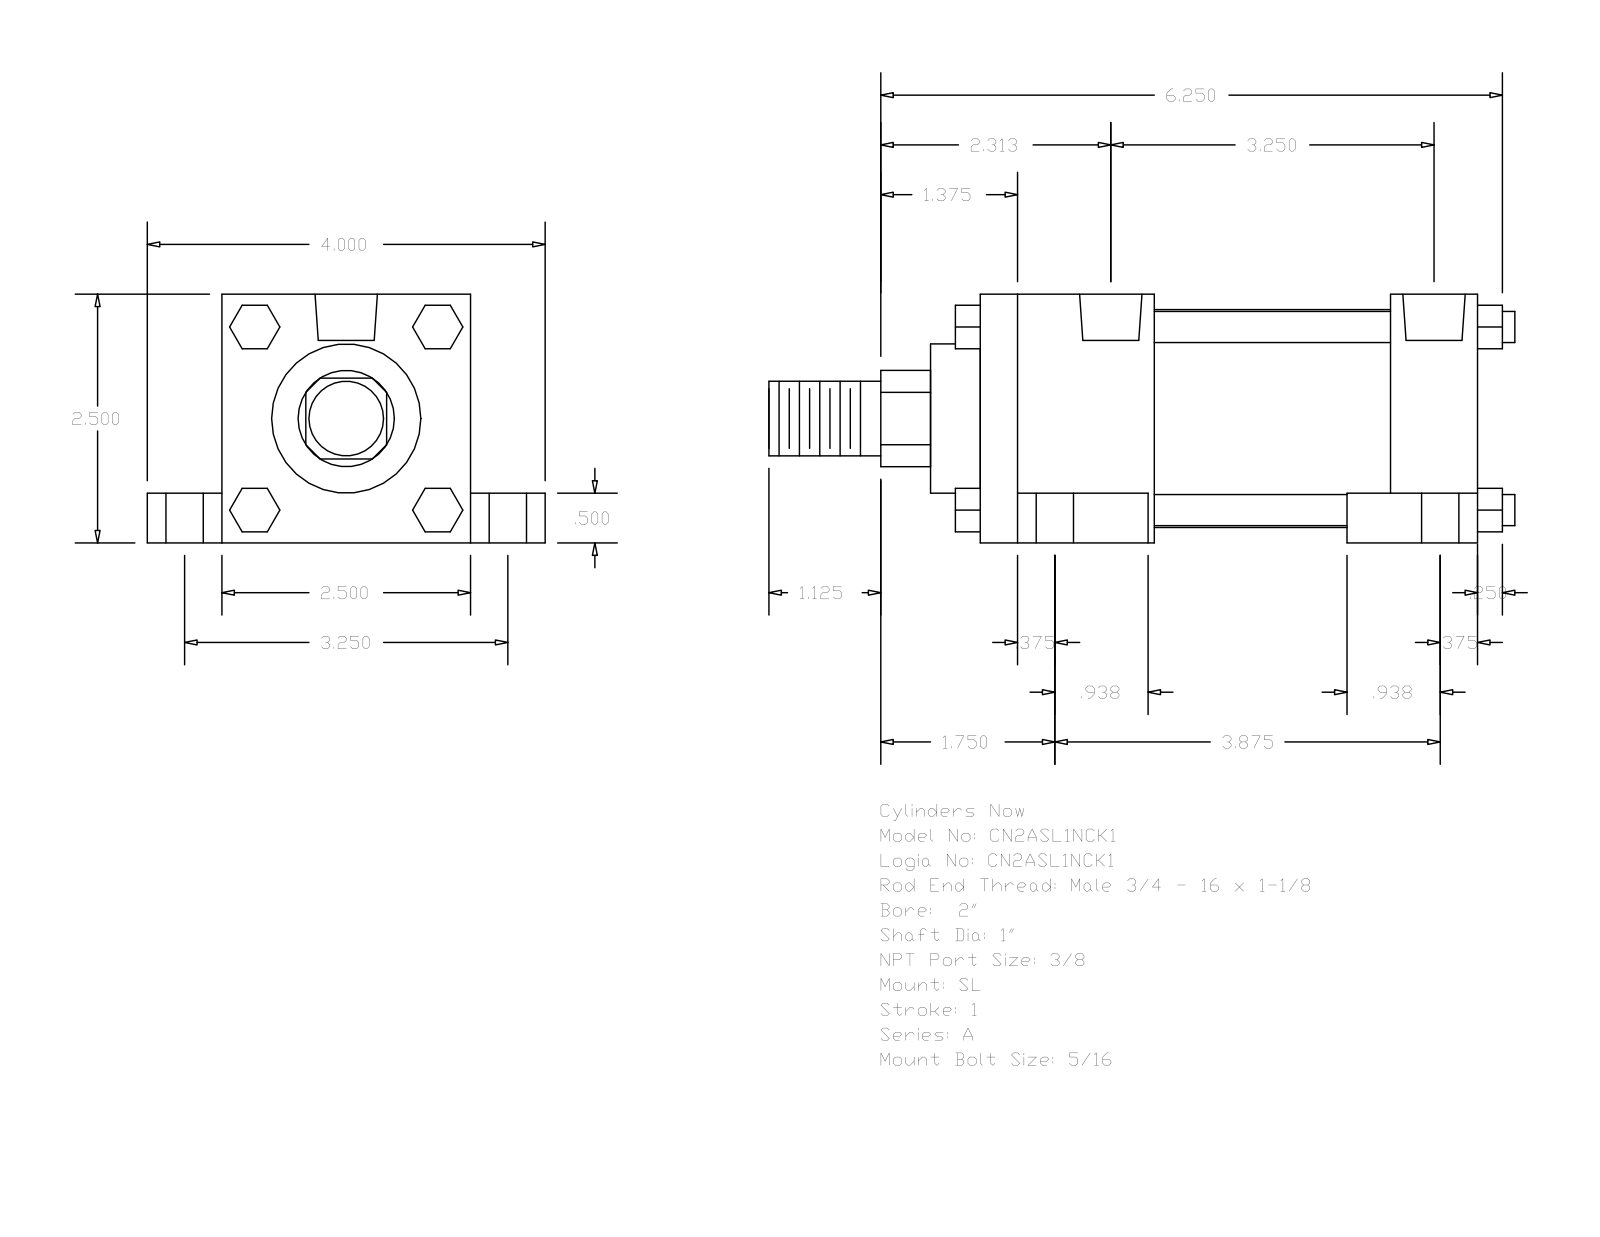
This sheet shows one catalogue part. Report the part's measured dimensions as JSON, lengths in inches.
{"part_name": "A_SL__0200_1", "step_written_by": "GSSL Pune (CONFIG_CONTROL_DESIGN)", "units": "inches", "bodies": {"solids": 0, "faces": 148, "planar": 112, "cylindrical": 36, "other": 0}, "overall_size": [7.5, 4, 2.5], "round_holes": [[0.219, 4], [0.375, 4], [0.625, 4], [0.627, 2]], "round_bosses_or_shafts": [[0.313, 4], [2.19, 1], [1.5, 1], [1, 1], [0.75, 1]], "partial_cylinders_radius": [[0.484, 1]], "face_to_face_distances": [2.5, 3.25, 0.5, 5, 2, 0.875, 0.75, 1.75, 4.125, 2.375], "hole_center_spacings": [1.626, 1.639, 1.719, 1.741, 3.031, 3.25, 3.633, 3.69]}
